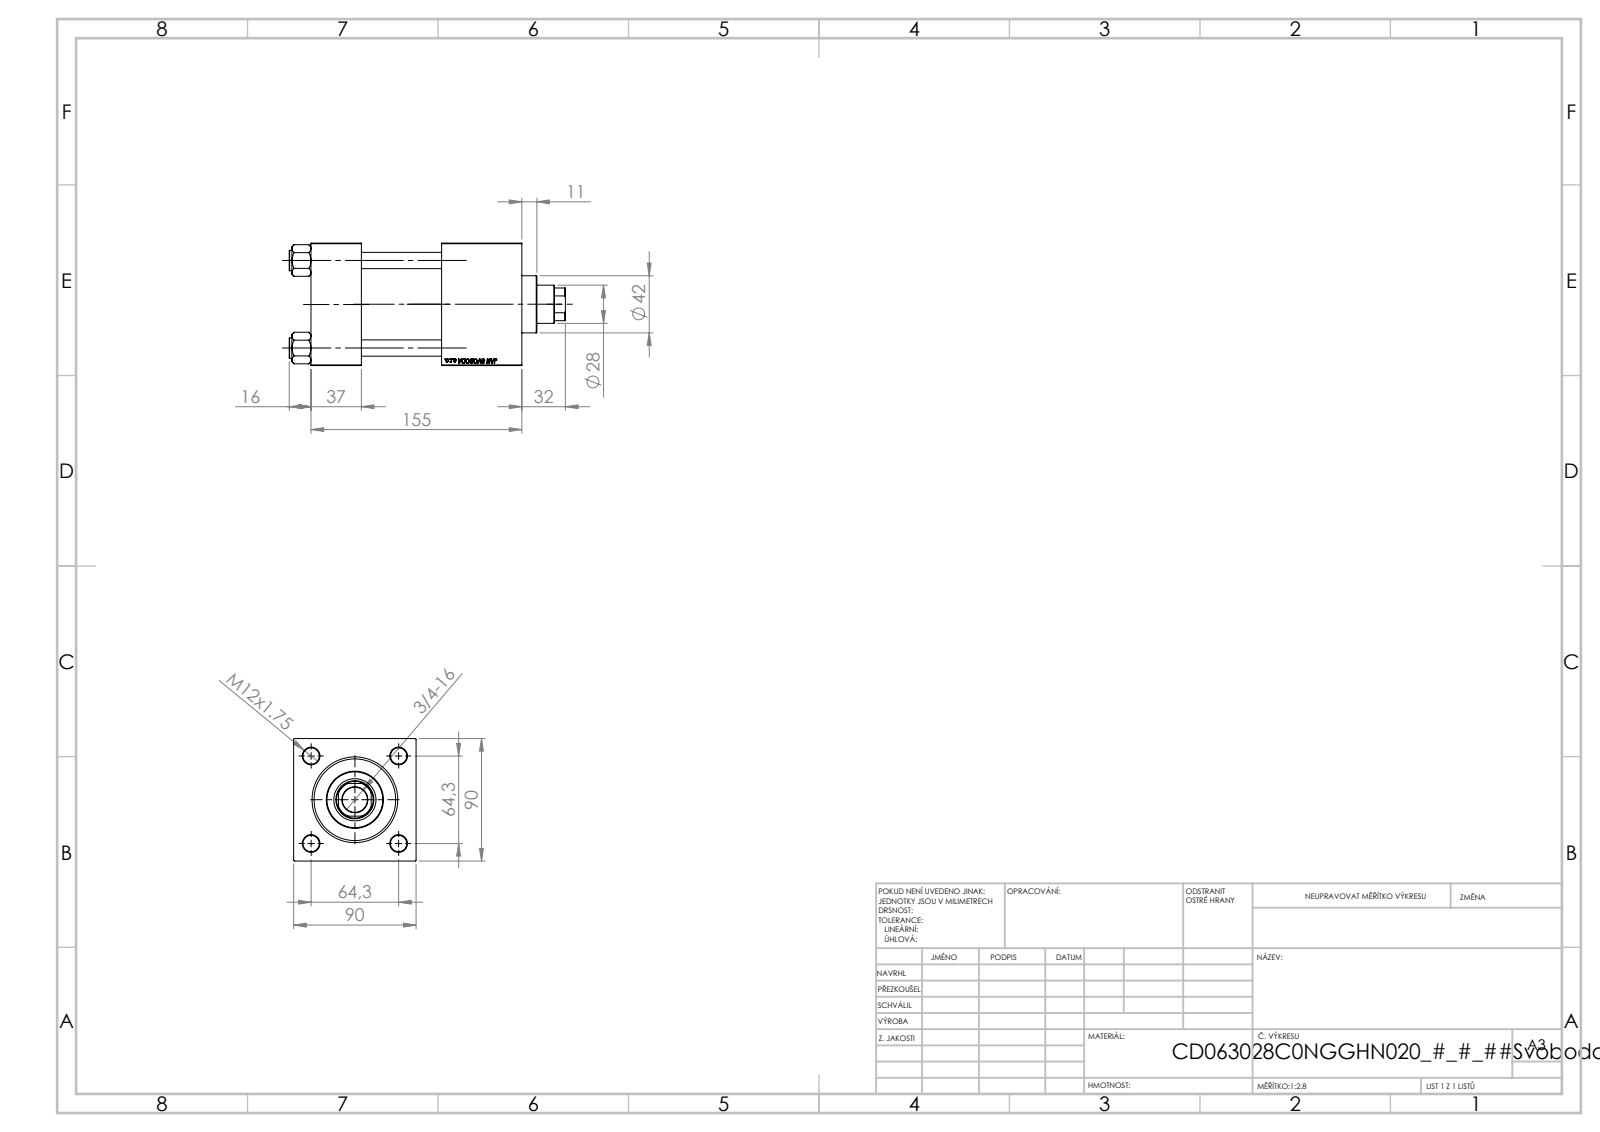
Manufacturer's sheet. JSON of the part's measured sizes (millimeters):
{"part_name": "V215CD_Body_C; NUT_M5_V215CD_C; V215CD_VC_C; V215CD_C_TYCINKA (+1 more)", "step_written_by": "SolidWorks 2019 (CONFIG_CONTROL_DESIGN)", "units": "millimeters", "bodies": {"solids": 11, "faces": 1149, "planar": 526, "cylindrical": 87, "other": 536}, "overall_size": [203, 90, 90], "volume_mm3": 946762, "surface_area_mm2": 179134, "round_holes": [[12, 4], [7, 2], [20.96, 2], [30, 2], [18.5, 1], [28, 1], [31, 1], [50, 1], [60, 1], [63, 1]], "round_bosses_or_shafts": [[15, 4], [69, 1], [42, 1]], "partial_cylinders_radius": [[13.5, 1]], "face_to_face_distances": [90, 59, 37, 155, 118, 96, 126.3, 89.3, 30.3, 28.7], "hole_center_spacings": [45.47, 64.3, 90.93, 97.5]}
